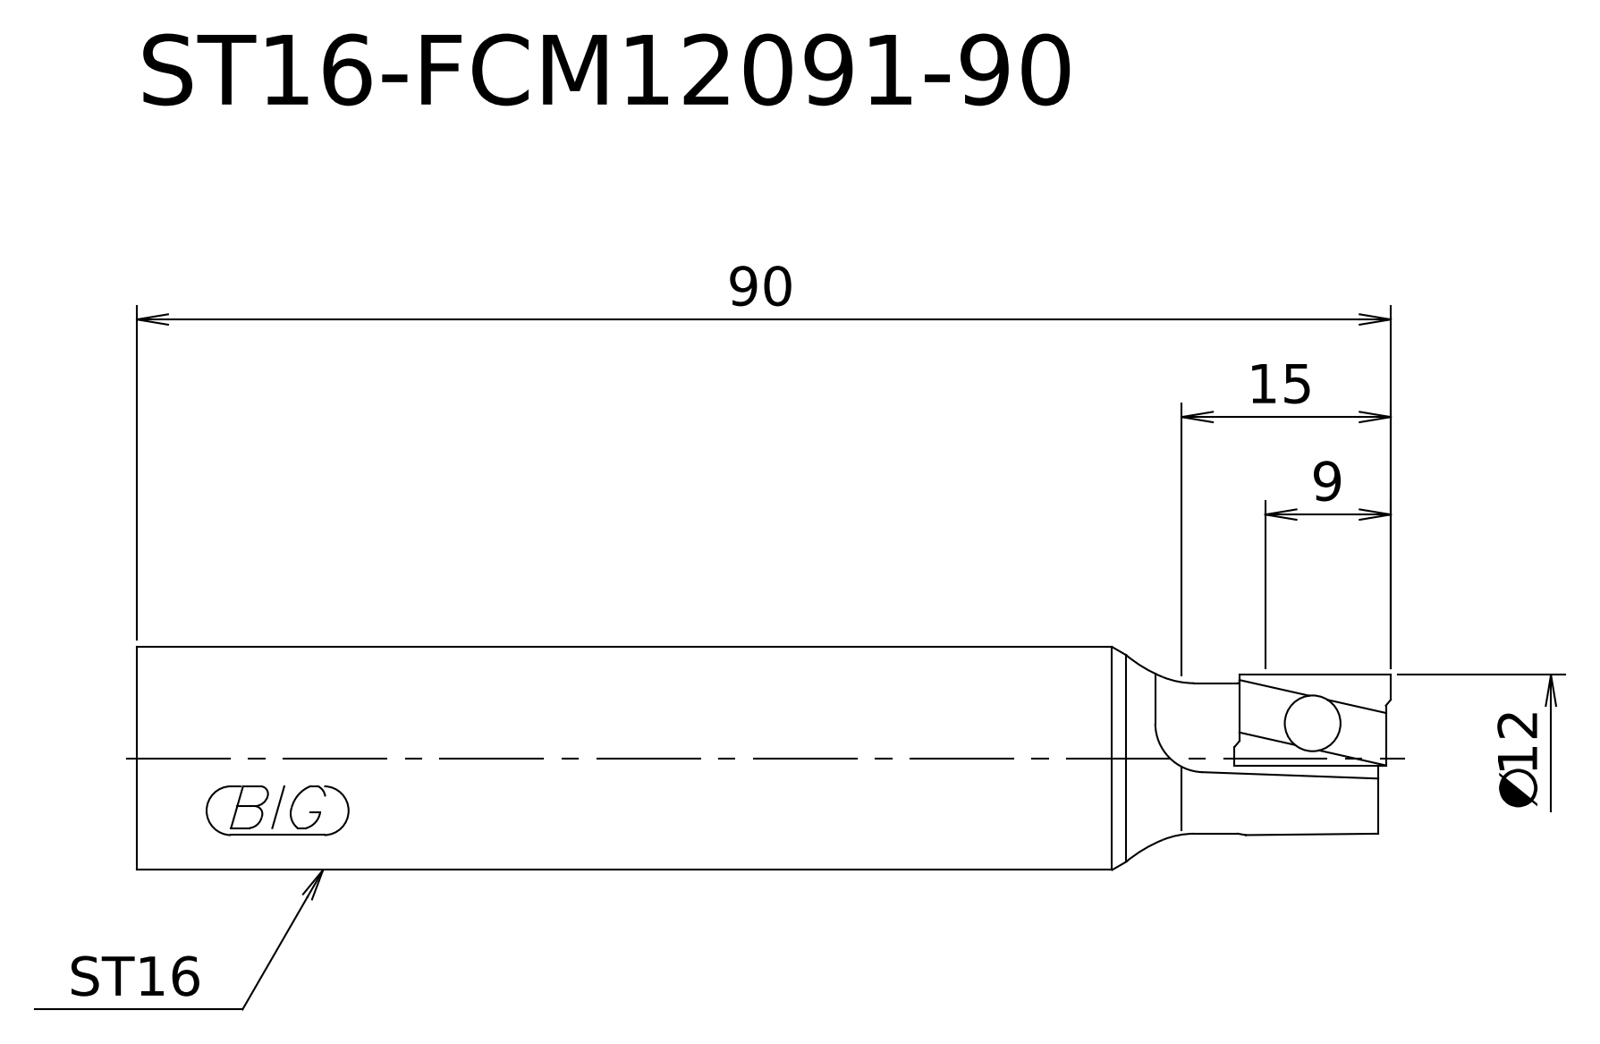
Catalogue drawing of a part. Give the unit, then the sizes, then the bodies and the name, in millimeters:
Units: millimetres
Overall size (bounding box): 90 × 16 × 16
Round bosses / shafts (diameter × count): ⌀16 ×1, ⌀12 ×1, ⌀10.8 ×1
Main face-to-face distances: 90, 10.86, 79.14
Volume: 16 442 mm³ · Surface area: 4 645 mm²
Bodies: 1 solid, 7 faces (3 planar, 3 cylindrical, 1 other)
STEP written by: Kubotek KeyCreator V8.5.1 (14335) (CONFIG_CONTROL_DESIGN)
